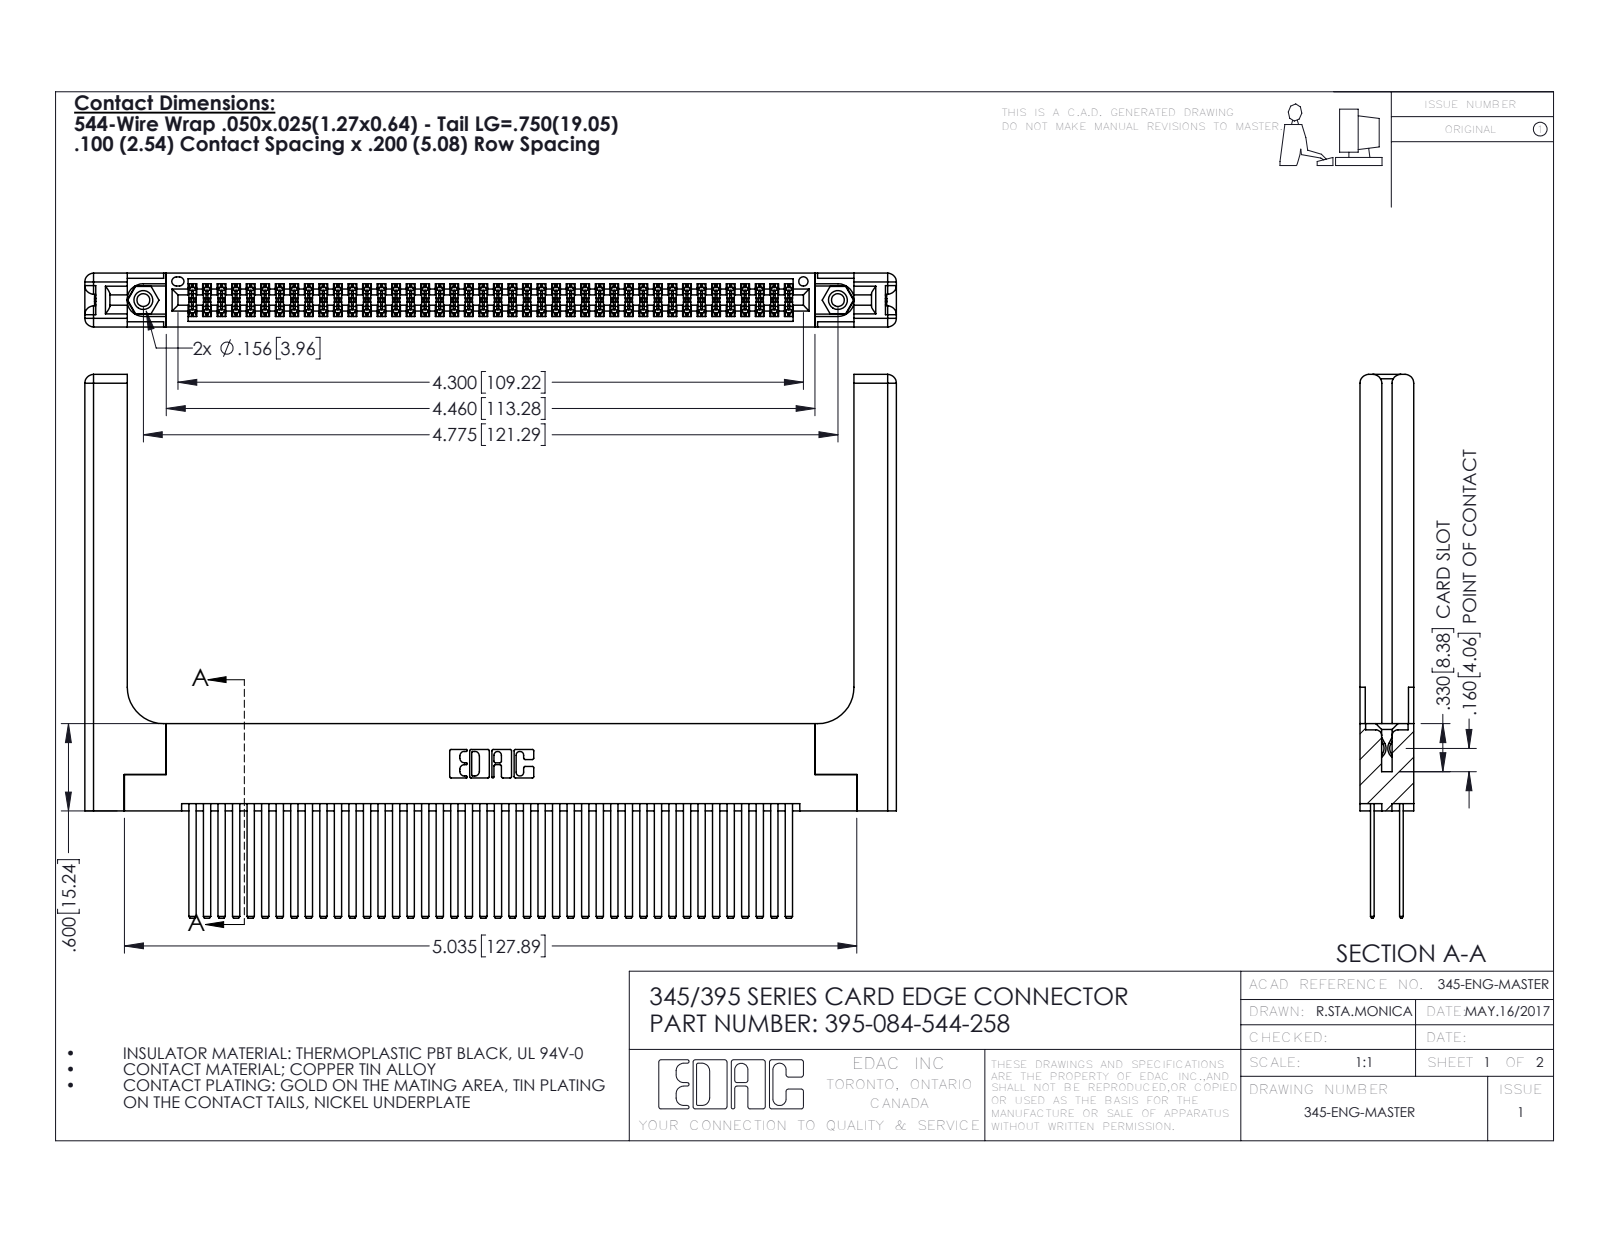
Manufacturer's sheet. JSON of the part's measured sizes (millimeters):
{"part_name": "345-220-058_345-220-058; 395-084-544-258; 345-250-001_345-250-001-102; 345 Part_Flush Mounting Lugs - 0.156 Dia-TH (+1 more)", "step_written_by": "SolidWorks 2016 (CONFIG_CONTROL_DESIGN)", "units": "millimeters", "bodies": {"solids": 89, "faces": 4078, "planar": 2664, "cylindrical": 1354, "other": 60}, "overall_size": [141.7, 94.9, 9.4], "volume_mm3": 23420, "surface_area_mm2": 30600, "round_holes": [[2.3, 2], [3.2, 2], [4, 2], [1.6, 1]], "round_bosses_or_shafts": [[3.9, 2]], "partial_cylinders_radius": [[0.2, 126], [0.3, 22], [1.5, 16], [0.2, 6], [0.8, 6], [0.7, 3], [0.4, 2], [0.5, 2]], "face_to_face_distances": [1.8, 7.6, 5.1, 2.5, 6.9, 0.6, 9.4, 5.7, 4.4, 3.8], "hole_center_spacings": [6.9, 115.3, 121.3]}
